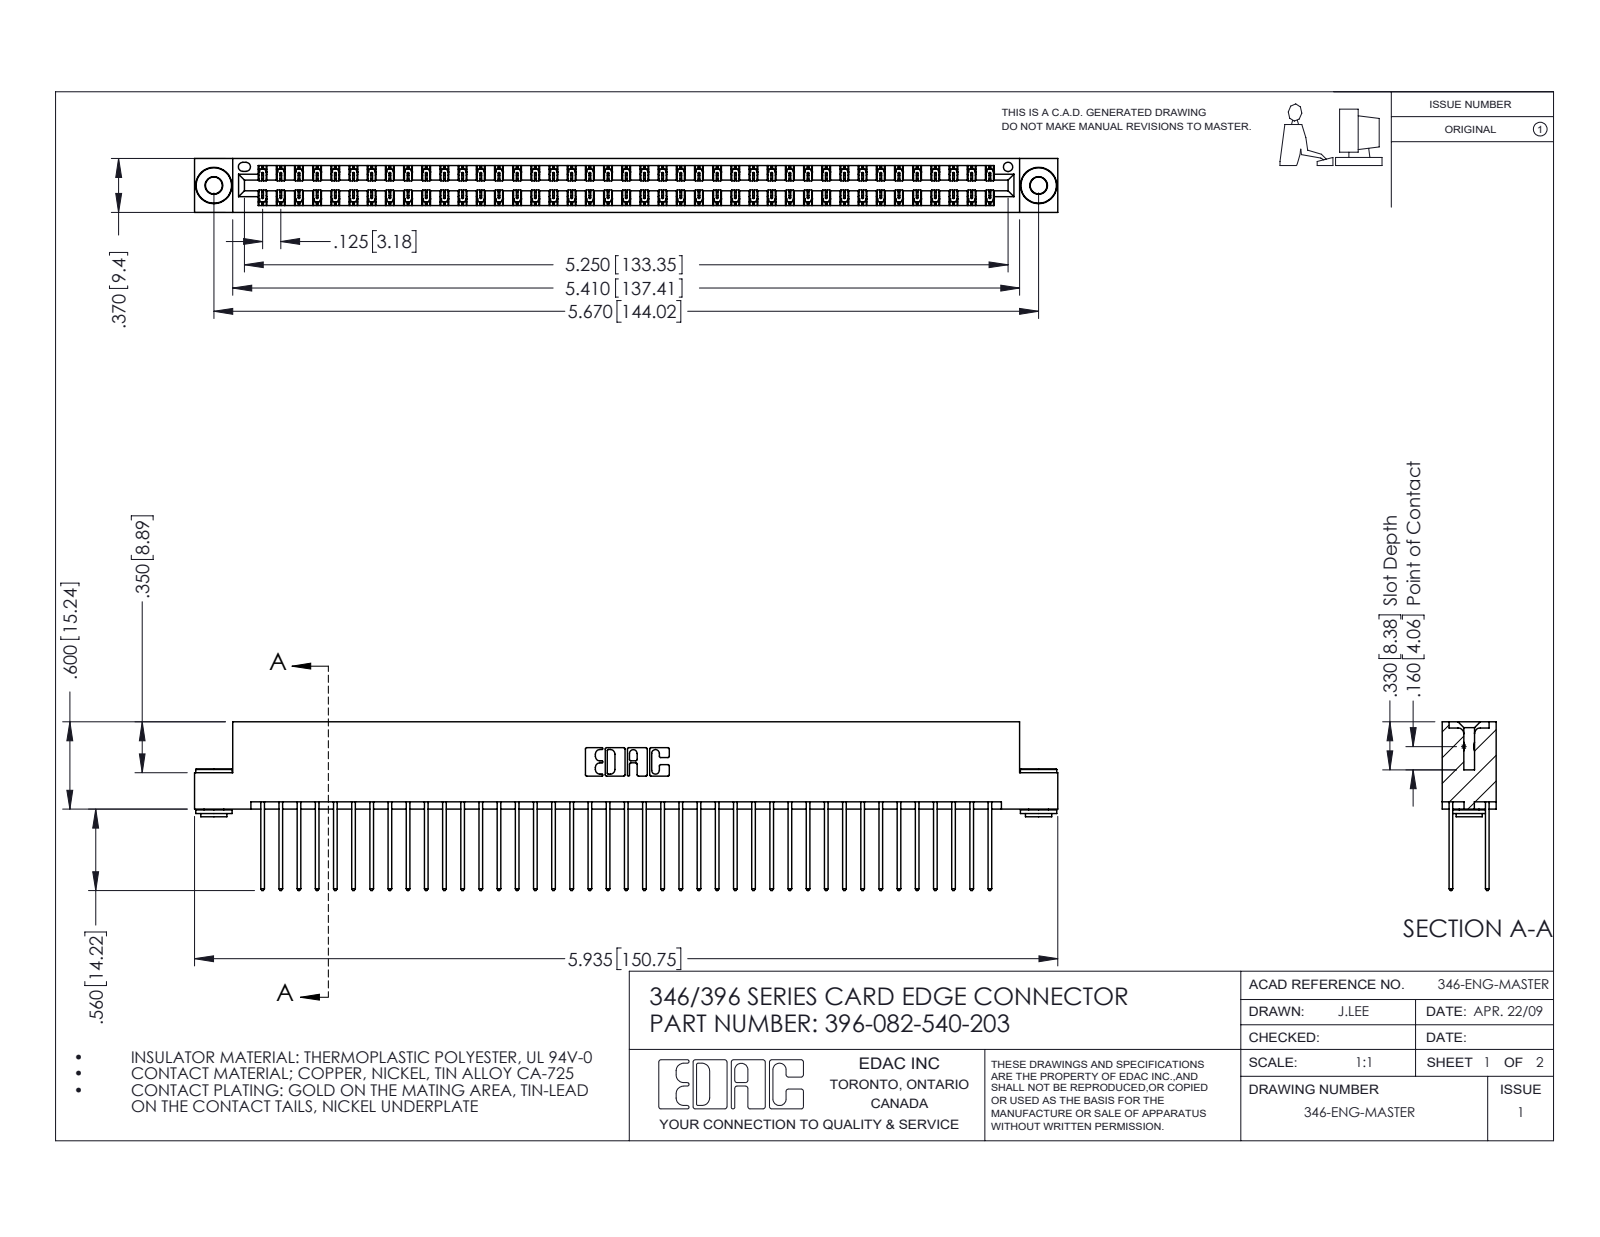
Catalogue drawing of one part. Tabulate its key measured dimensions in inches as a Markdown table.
| quantity | value |
| --- | --- |
| part name | 345-250-002_345-250-002-102; 346 Part_Flush Mounting Lugs - 0.156 Dia-TH; 345-292-001_345-293-140; 396-082-540-203 |
| STEP written by | SolidWorks 2016 (CONFIG_CONTROL_DESIGN) |
| units | inches |
| bodies | 85 solids, 4424 faces (2956 planar, 1460 cylindrical, 8 other) |
| overall size | 5.935 × 1.16 × 0.37 |
| volume | 0.917 in³ |
| surface area | 34.59 in² |
| round holes (diameter × count) | 0.116 × 2, 0.156 × 2, 0.064 × 1 |
| round bosses / shafts (diameter × count) | 0.25 × 2, 0.18 × 2, 0.136 × 2 |
| partial cylindrical surfaces (radius × count) | 0.006 × 123, 0.01 × 82, 0.01 × 22, 0.007 × 6, 0.031 × 6, 0.026 × 3, 0.014 × 2, 0.022 × 2 |
| main face-to-face distances | 0.048, 0.322, 0.25, 0.025, 0.072, 0.298, 0.37, 0.275, 0.148, 0.222 |
| hole center spacings | 0.246, 5.461, 5.67 |
